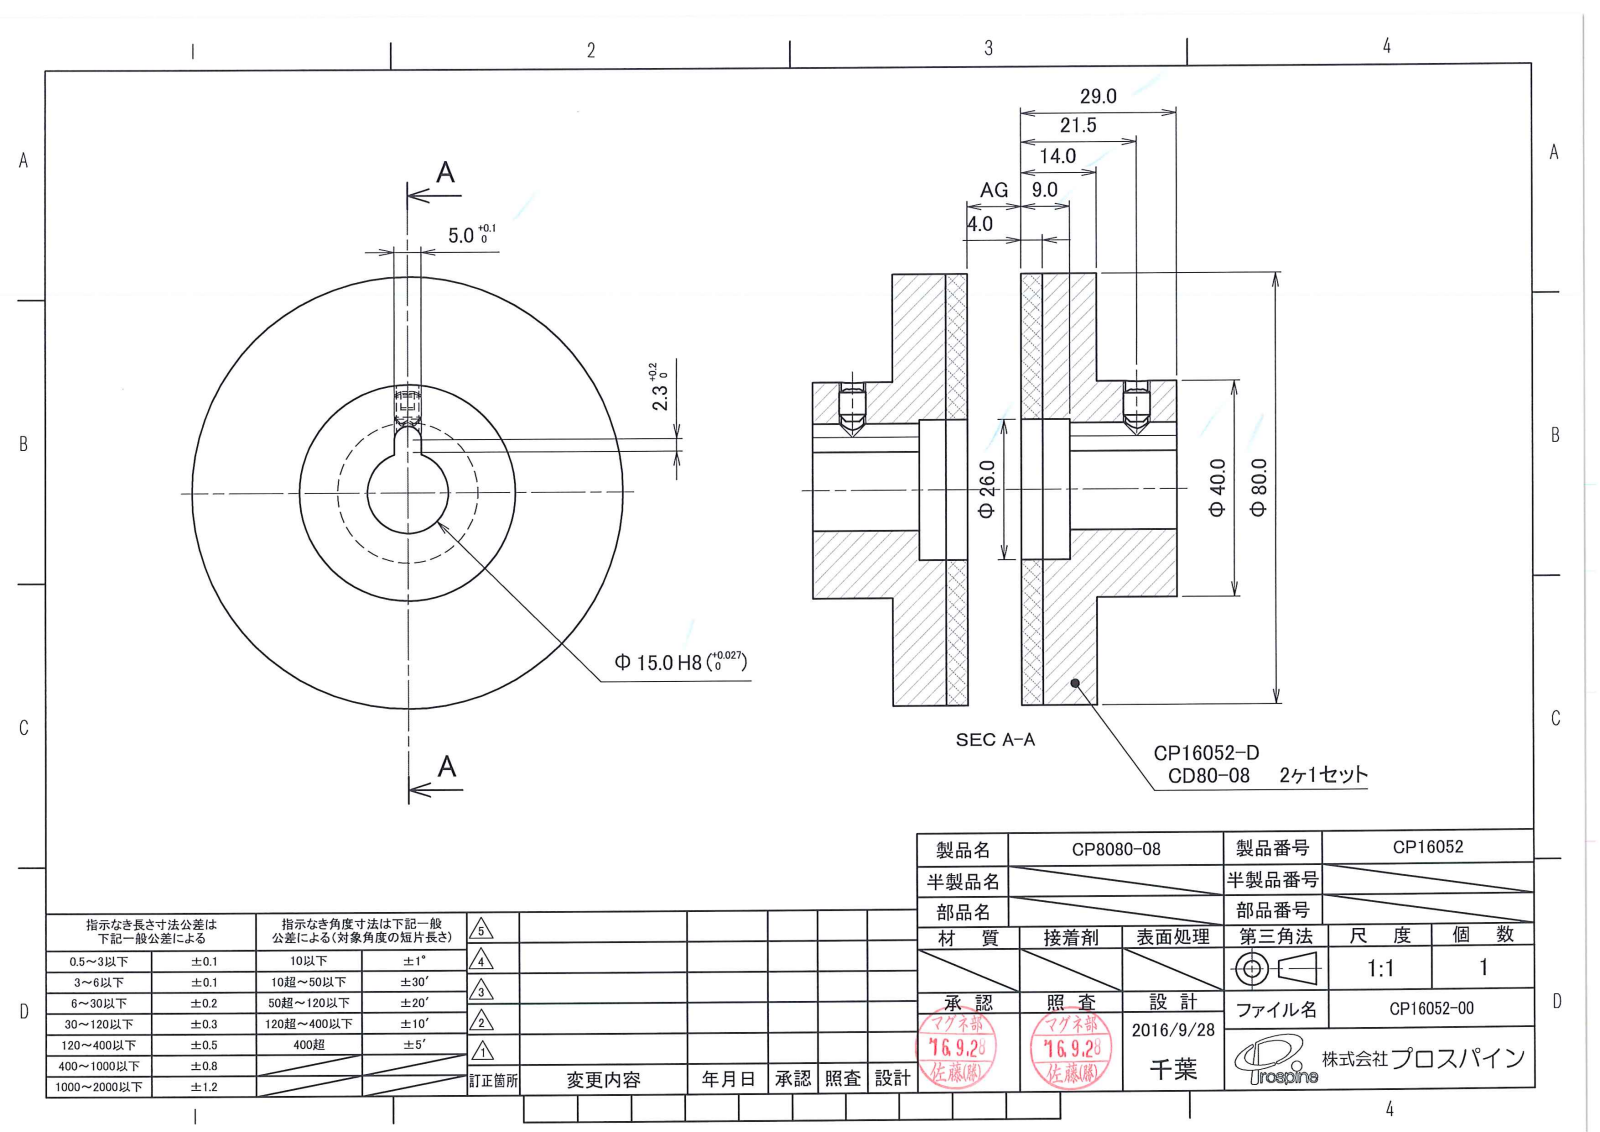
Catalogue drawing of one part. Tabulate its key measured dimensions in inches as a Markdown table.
| quantity | value |
| --- | --- |
| STEP written by | PSStep 10.0 (CONFIG_CONTROL_DESIGN) |
| units | inches |
| bodies | 4 solids, 38 faces (22 planar, 10 cylindrical, 6 other) |
| overall size | 3.15 × 3.15 × 1.142 |
| volume | 4.914 in³ |
| surface area | 40.68 in² |
| round holes (diameter × count) | 0.165 × 1, 0.591 × 1, 1.024 × 1 |
| round bosses / shafts (diameter × count) | 3.15 × 1, 1.575 × 1, 0.197 × 1 |
| partial cylindrical surfaces (radius × count) | 0.098 × 1 |
| main face-to-face distances | 0.157, 0.551, 0.394, 1.142, 0.984, 0.591, 0.197, 0.354, 0.787, 0.098 |
